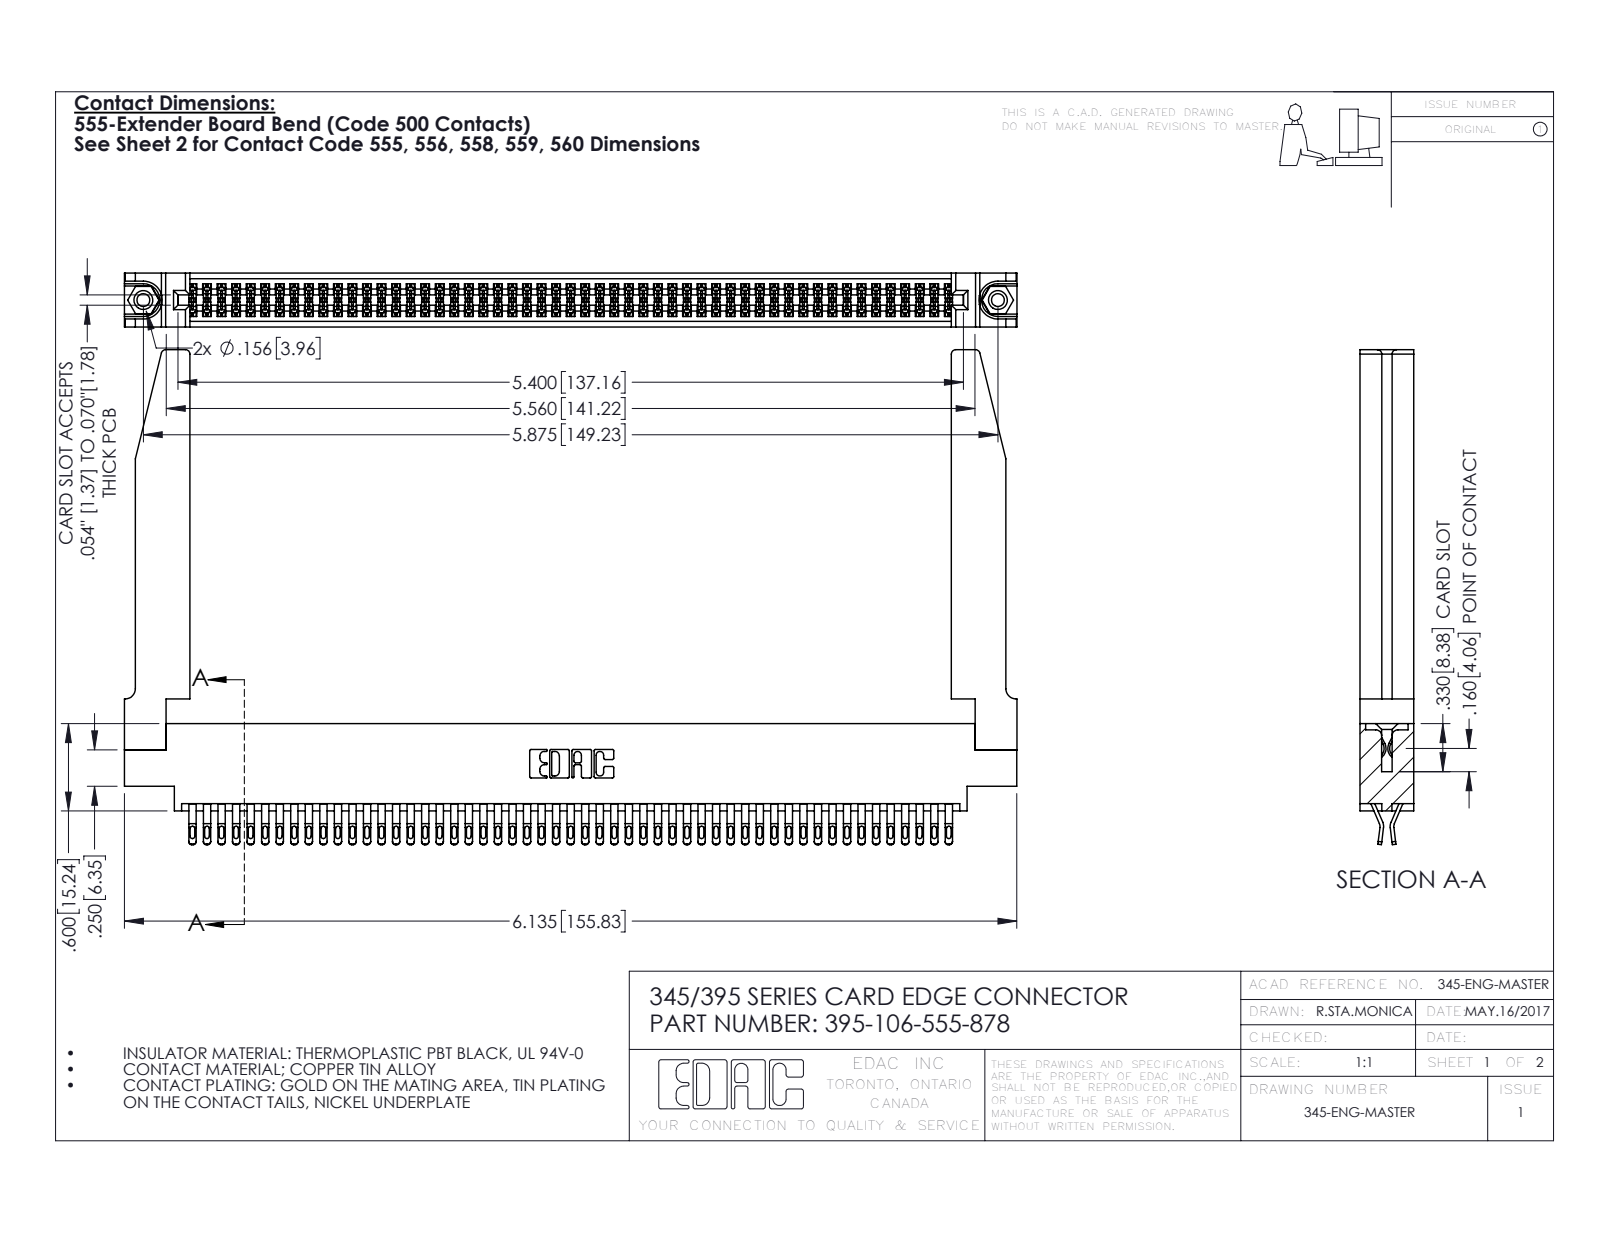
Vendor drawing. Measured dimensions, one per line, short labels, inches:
name: 345-292-001_555 Tail; 345-220-078_345-220-078; 345-250-001_345-250-001-102; 395-106-555-878 (+1 more)
written by: SolidWorks 2016 (CONFIG_CONTROL_DESIGN)
unit: in
bodies: 111 solids, 6300 faces (3512 planar, 2736 cylindrical, 52 other)
size: 6.136 × 3.402 × 0.37
volume: 1.416 in³; area: 48.18 in²
holes: 2× ⌀0.089, 2× ⌀0.125, 2× ⌀0.156, 1× ⌀0.064
bosses: 2× ⌀0.155
rounds: 265× R0.016, 212× R0.02, 159× R0.006, 22× R0.01, 8× R0.03, 6× R0.007, 6× R0.031, 3× R0.026
face distances: 0.37, 0.072, 0.298, 0.025, 0.098, 0.272, 0.2, 0.225, 0.175, 0.148
hole spacings: 0.27, 5.639, 5.875
